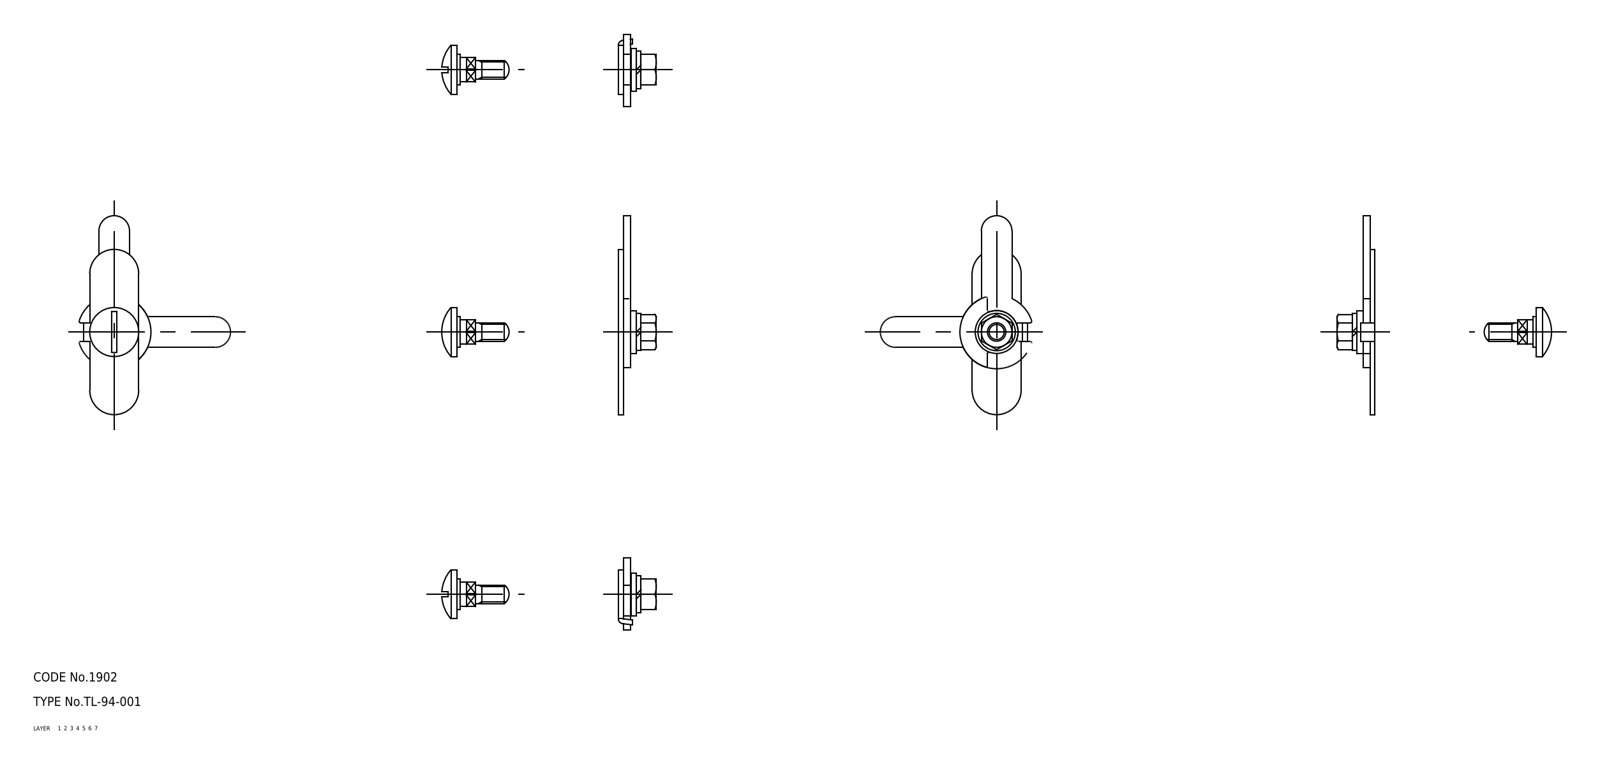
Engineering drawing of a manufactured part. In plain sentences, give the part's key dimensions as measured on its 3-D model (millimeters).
The part is named "cam; washer; nut; knob (+2 more)". Its 3-D file was written by "CADfix (AUTOMOTIVE_DESIGN)". It is 5 solids with 91 faces: 0 planar, 0 cylindrical and 91 other. Overall it measures 65 by 23.45 by 21.97 millimeters. Its volume is 4 463 cubic millimeters and its surface area 5 105 square millimeters.
